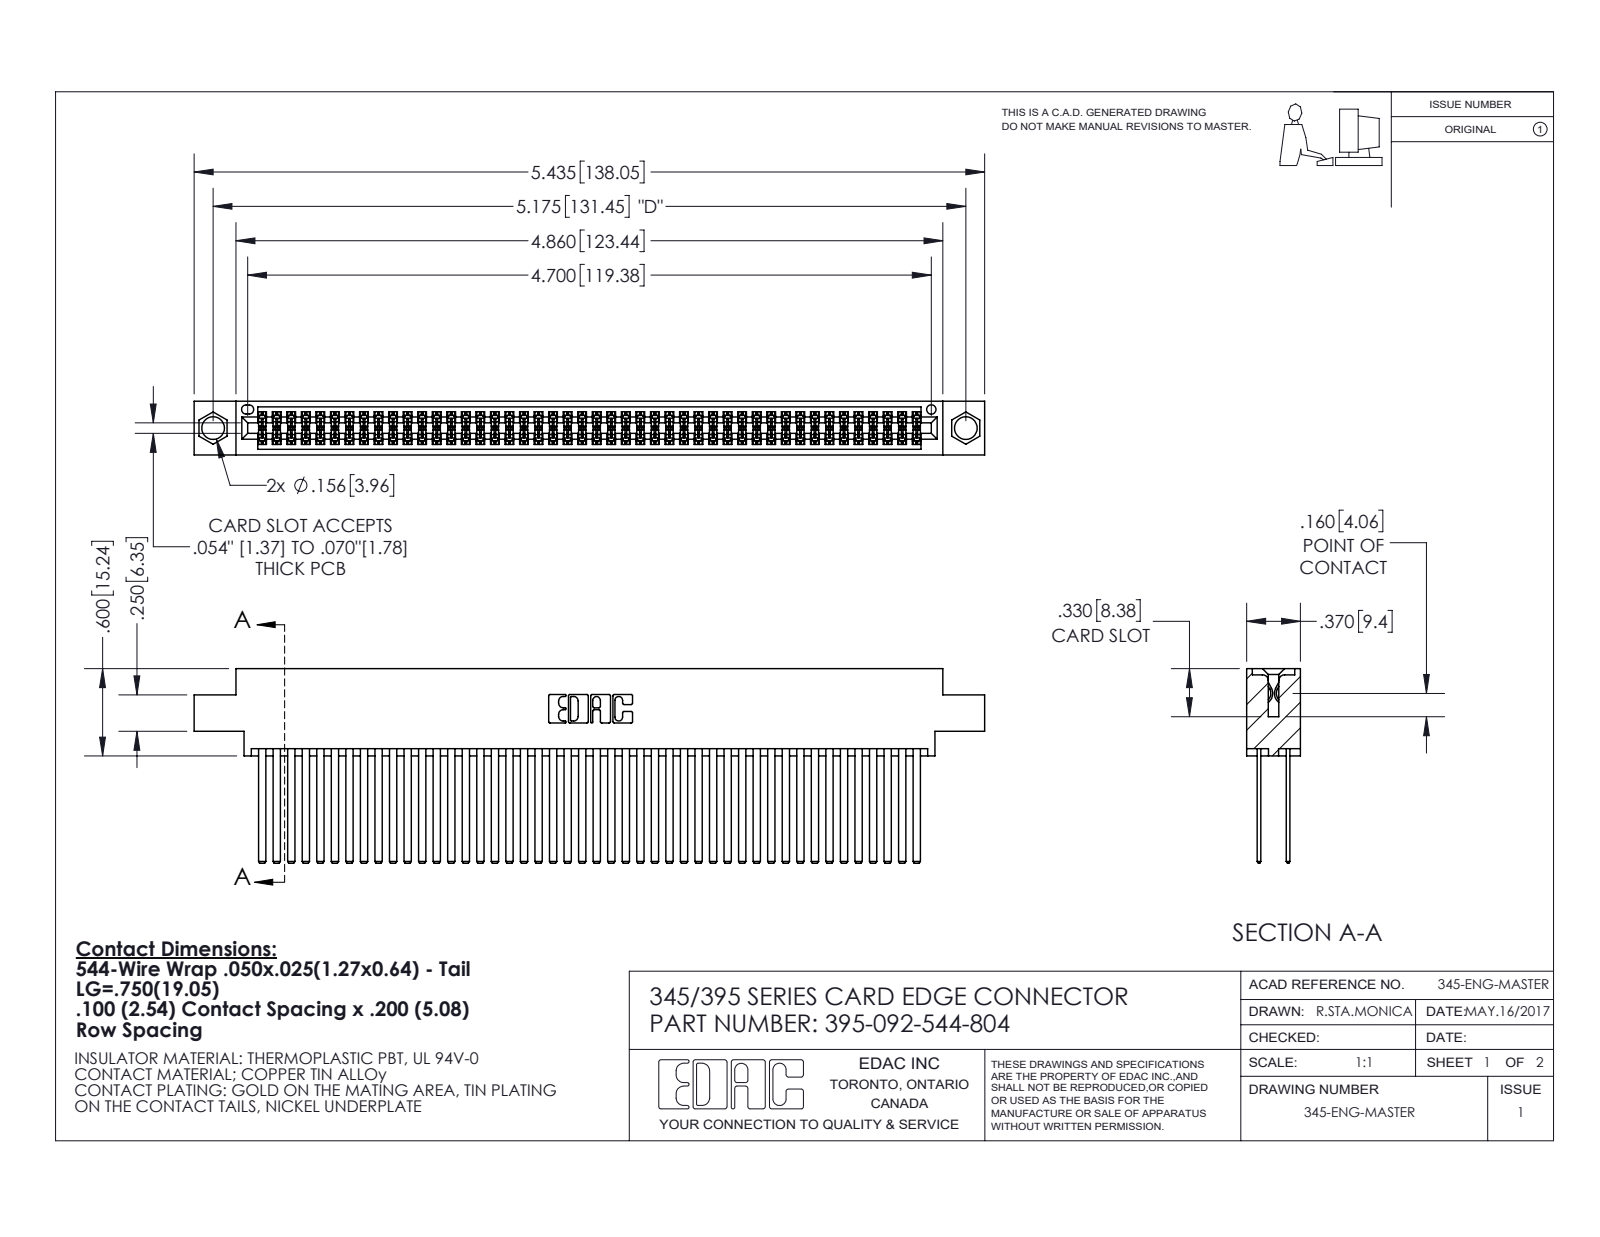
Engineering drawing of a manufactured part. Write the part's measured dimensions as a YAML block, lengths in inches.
part_name: "345-292-001_345-293-144; 345 Part_0.170 Offset - 0.156 Dia-TI; 395-092-544-804"
step_written_by: "SolidWorks 2020 (CONFIG_CONTROL_DESIGN)"
units: inches
bodies: {solids: 93, faces: 4192, planar: 2766, cylindrical: 1426, other: 0}
overall_size: [5.435, 1.337, 0.37]
volume: 0.886
surface_area: 39.23
round_holes:
  - {diameter: 0.156, count: 2}
  - {diameter: 0.064, count: 1}
partial_cylinders:
  - {radius: 0.006, count: 138}
  - {radius: 0.01, count: 22}
  - {radius: 0.007, count: 6}
  - {radius: 0.031, count: 6}
  - {radius: 0.026, count: 3}
  - {radius: 0.014, count: 2}
  - {radius: 0.019, count: 2}
  - {radius: 0.022, count: 2}
face_to_face_distances: [0.2, 0.025, 0.072, 0.098, 0.272, 0.298, 0.225, 0.175, 0.37, 0.15]
hole_center_spacings: [0.27, 4.939, 5.175]
